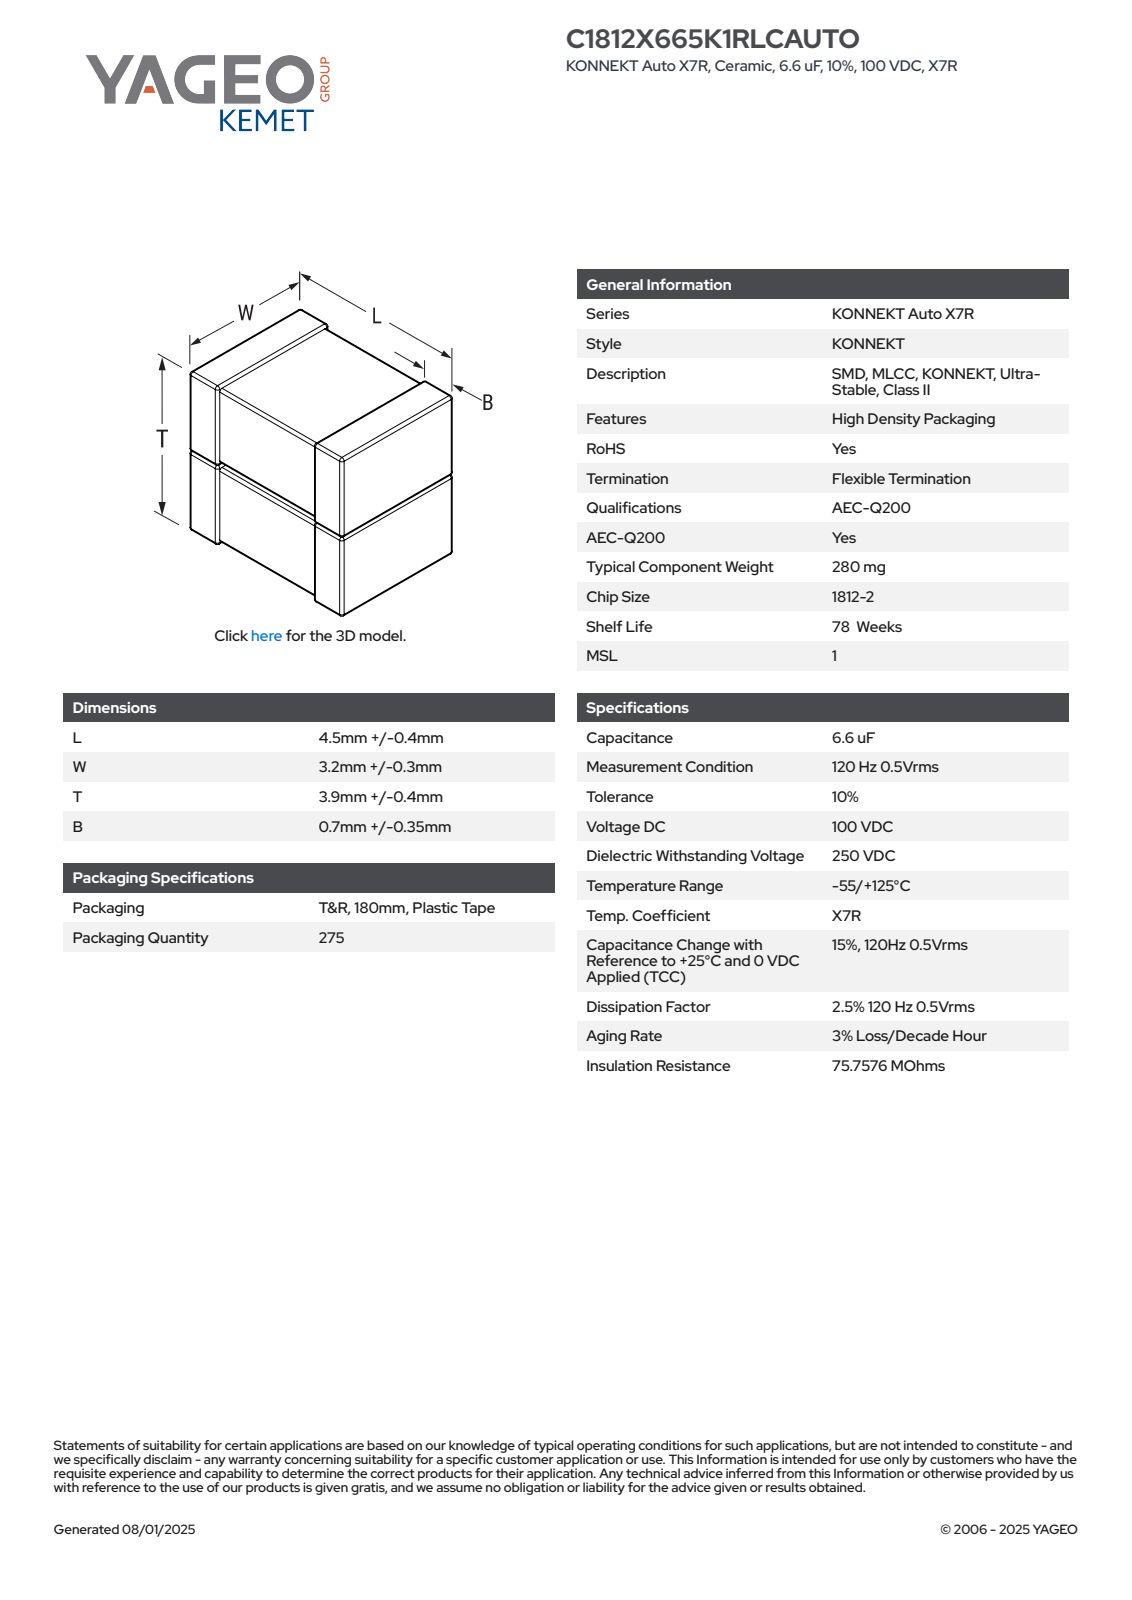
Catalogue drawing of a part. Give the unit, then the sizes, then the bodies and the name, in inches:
Units: inches
Overall size (bounding box): 0.193 × 0.169 × 0.138
Main face-to-face distances: 0.079, 0.085, 0.135, 0.193, 0.082, 0.087, 0.167, 0.132, 0.164, 0.138
Volume: 0.004 in³ · Surface area: 0.195 in²
Bodies: 4 solids, 197 faces (81 planar, 84 cylindrical, 32 other)
Part name (STEP PRODUCT): CCSS_K2T_1812-2_L4.9W3.5B1.05T4.3
STEP written by: SolidWorks 2020 (AUTOMOTIVE_DESIGN)
